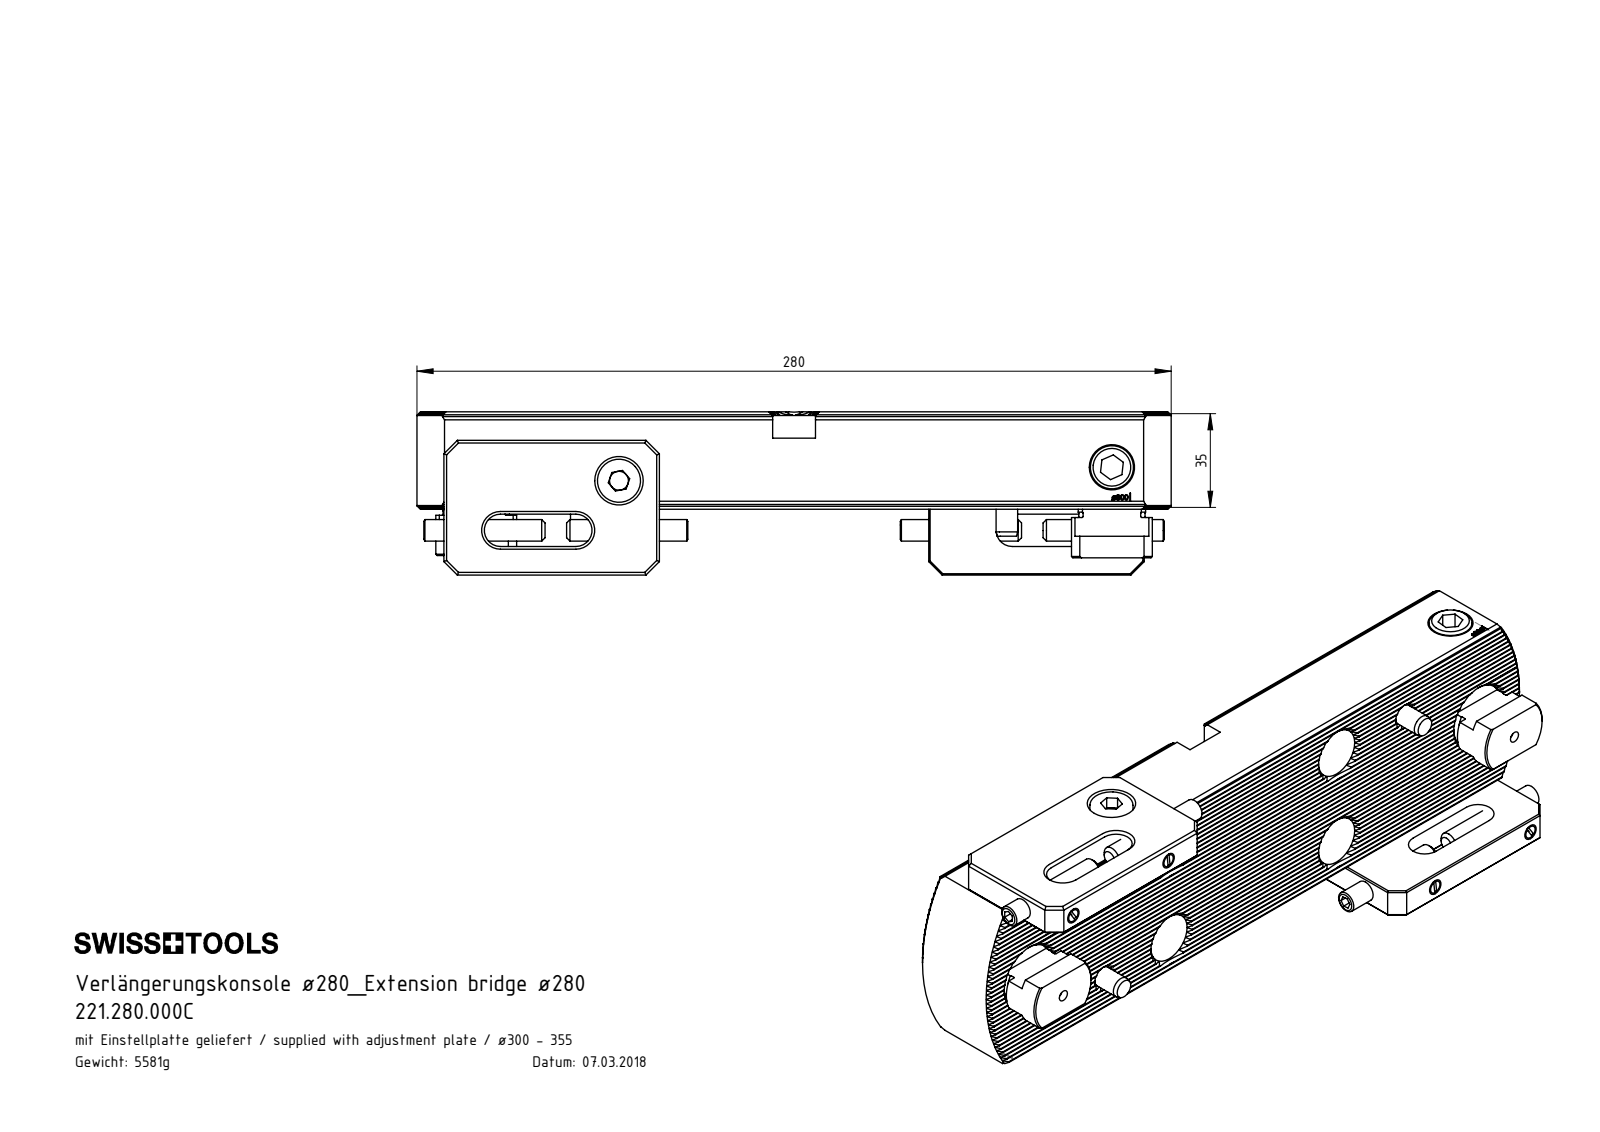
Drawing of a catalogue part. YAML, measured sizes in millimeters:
part_name: "VK1-ER2.201.010_A_vorgespannt; VK1-ER2.201.010_A_gespannt; VK1-ER2.101.010_A; VK1-ER2.001.044_A (+8 more)"
step_written_by: "SolidWorks 2017 (CONFIG_CONTROL_DESIGN)"
units: millimeters
bodies: {solids: 27, faces: 1787, planar: 975, cylindrical: 477, other: 335}
overall_size: [280, 94, 60.58]
volume: 716990
surface_area: 152062
round_holes:
  - {diameter: 5, count: 4}
  - {diameter: 6, count: 4}
  - {diameter: 6.8, count: 4}
  - {diameter: 13, count: 4}
  - {diameter: 19, count: 4}
  - {diameter: 2, count: 2}
  - {diameter: 8, count: 2}
  - {diameter: 8.5, count: 2}
  - {diameter: 10.5, count: 2}
  - {diameter: 11, count: 2}
  - {diameter: 14, count: 2}
  - {diameter: 18, count: 2}
round_bosses_or_shafts:
  - {diameter: 16, count: 4}
  - {diameter: 6, count: 4}
  - {diameter: 10, count: 2}
  - {diameter: 8, count: 2}
partial_cylinders:
  - {radius: 0.14, count: 66}
  - {radius: 2, count: 8}
  - {radius: 6, count: 4}
  - {radius: 12.3, count: 2}
  - {radius: 15, count: 2}
  - {radius: 65, count: 2}
  - {radius: 7.95, count: 1}
face_to_face_distances: [70, 1.73, 12, 82, 16.64, 3.46, 51.96, 0.5, 11.5, 82.5]
hole_center_spacings: [76.66, 163.23, 236, 7.9, 18.55, 19.61, 33.42, 34.53]
